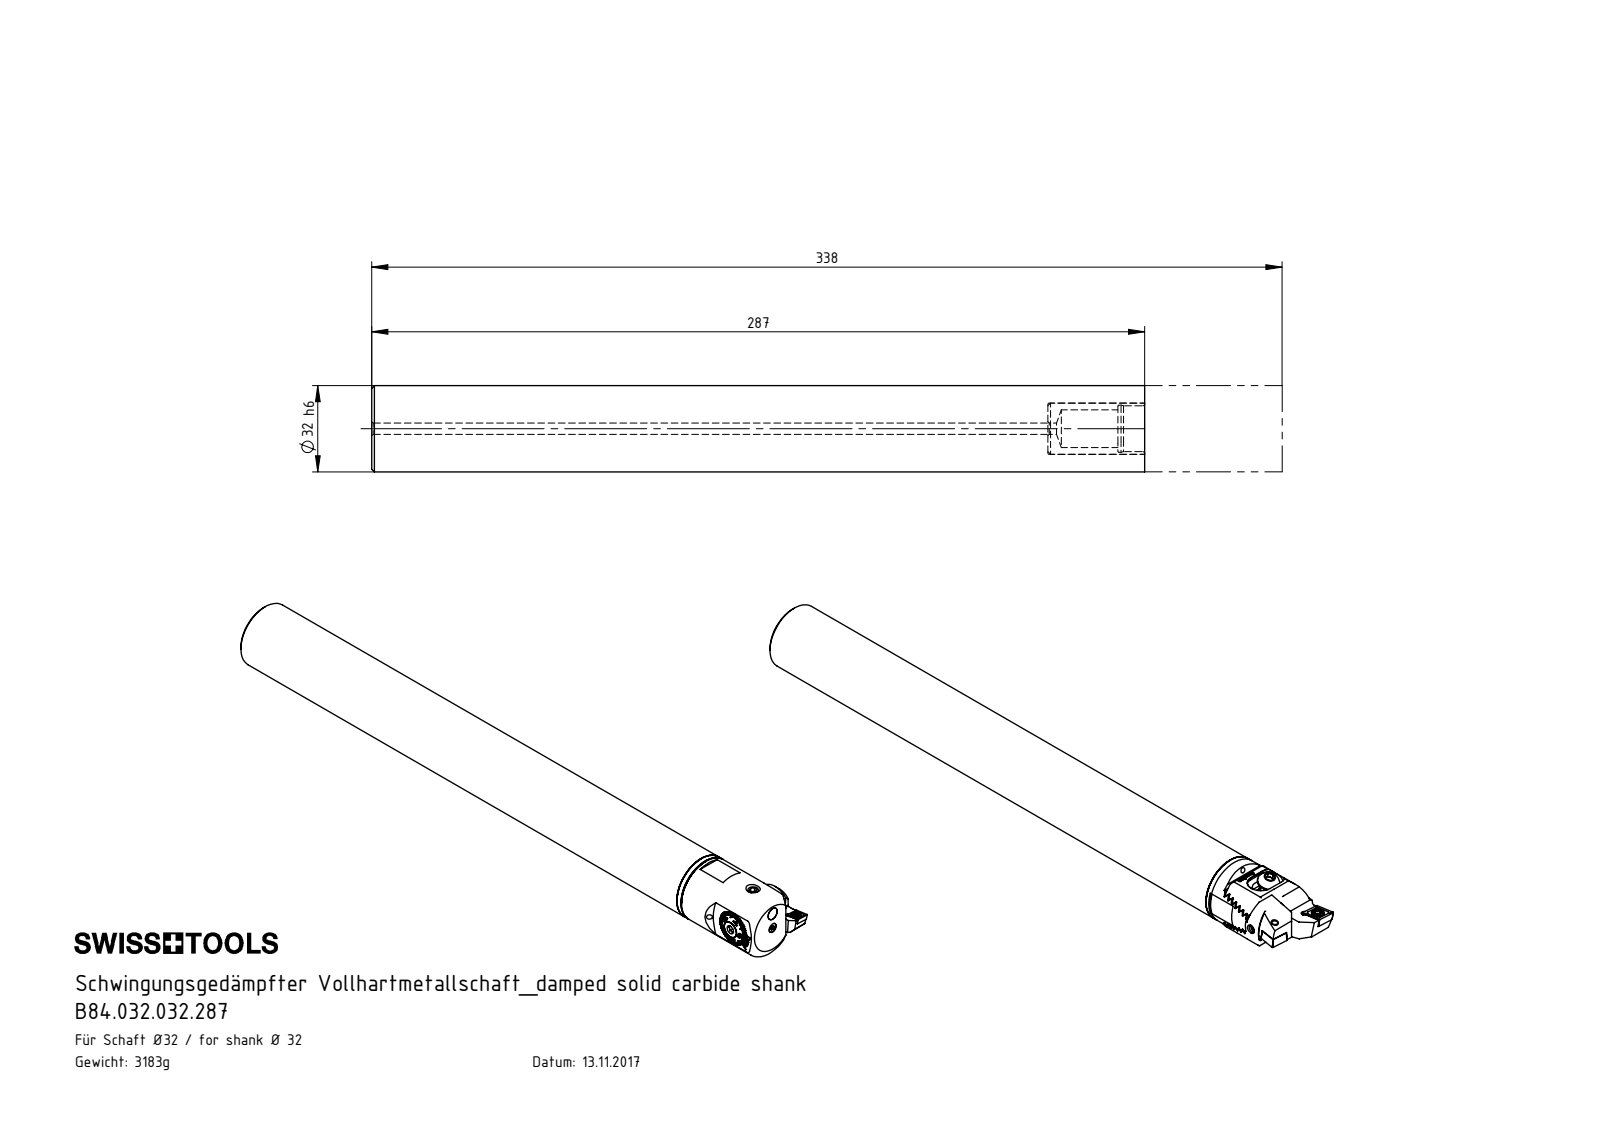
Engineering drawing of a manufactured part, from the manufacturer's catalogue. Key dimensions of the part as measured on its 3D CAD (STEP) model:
Part name (STEP PRODUCT): HP5-Z32.040.051_fr Zeichnung; Z32-WCB.001.021; Z32-ER3.001.013_A; CCMT09T304 (+8 more)
STEP written by: SolidWorks 2017 (CONFIG_CONTROL_DESIGN)
Units: millimetres
Bodies: 18 solids, 1025 faces (463 planar, 248 cylindrical, 314 other)
Overall size (bounding box): 335 × 40 × 32
Volume: 253 763 mm³ · Surface area: 59 563 mm²
Round holes (diameter × count): ⌀2.5 ×5, ⌀3.3 ×5, ⌀1.6 ×2, ⌀2 ×2, ⌀4.4 ×2, ⌀5 ×2, ⌀6.1 ×2, ⌀6.4 ×2, ⌀6.8 ×2, ⌀3.5 ×1, ⌀4.2 ×1, ⌀10.2 ×1
Round bosses / shafts (diameter × count): ⌀4 ×4, ⌀10.5 ×2, ⌀10.2 ×2, ⌀6 ×2, ⌀5.25 ×2, ⌀32 ×1, ⌀16 ×1, ⌀12 ×1
Partial cylindrical surfaces — rounded edges, fillets, slot ends (radius × count): R0.5 ×16, R0.2 ×14, R0.2 ×12, R0.34 ×12, R0.59 ×12, R2 ×4, R3.3 ×4, R6 ×4
Main face-to-face distances: 2.38, 4.76, 7.14, 287, 9.52, 3, 290, 36, 251, 39
Hole centre spacings: 6.07, 6.19, 24.22, 24.33, 28.65, 9, 9.01, 17.39
